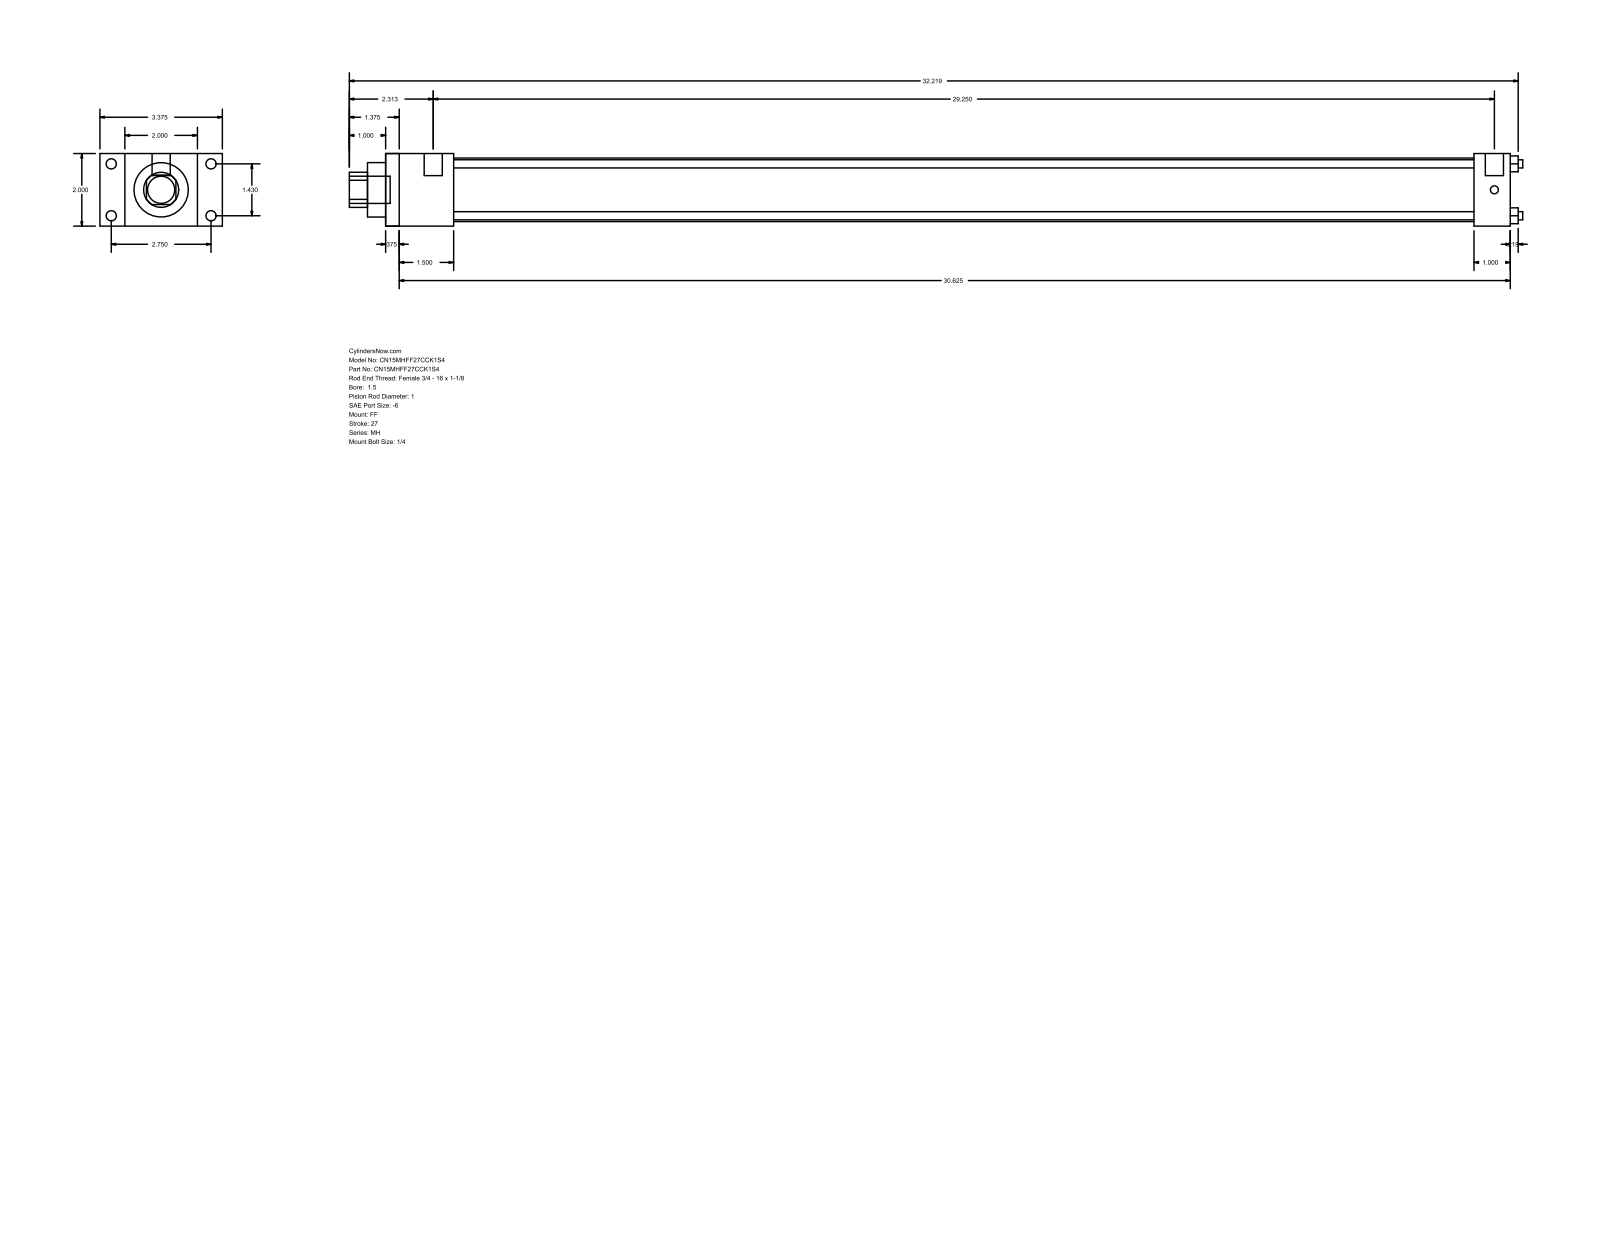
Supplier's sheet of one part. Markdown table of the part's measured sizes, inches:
| quantity | value |
| --- | --- |
| part name | MH_FF__0150_1 |
| STEP written by | GSSL Pune (CONFIG_CONTROL_DESIGN) |
| units | inches |
| bodies | 0 solids, 92 faces (64 planar, 28 cylindrical, 0 other) |
| overall size | 32.344 × 3.375 × 2 |
| round holes (diameter × count) | 0.225 × 4, 1 × 1, 1.5 × 1, 1.75 × 1 |
| round bosses / shafts (diameter × count) | 0.281 × 4, 0.219 × 4, 0.5 × 2, 0.75 × 1 |
| partial cylindrical surfaces (radius × count) | 0.484 × 1 |
| main face-to-face distances | 2, 31, 0.375, 30.625, 1, 0.687, 2.687, 1.875, 1.5, 29.125 |
| hole center spacings | 1.011, 1.43, 2.022 |
